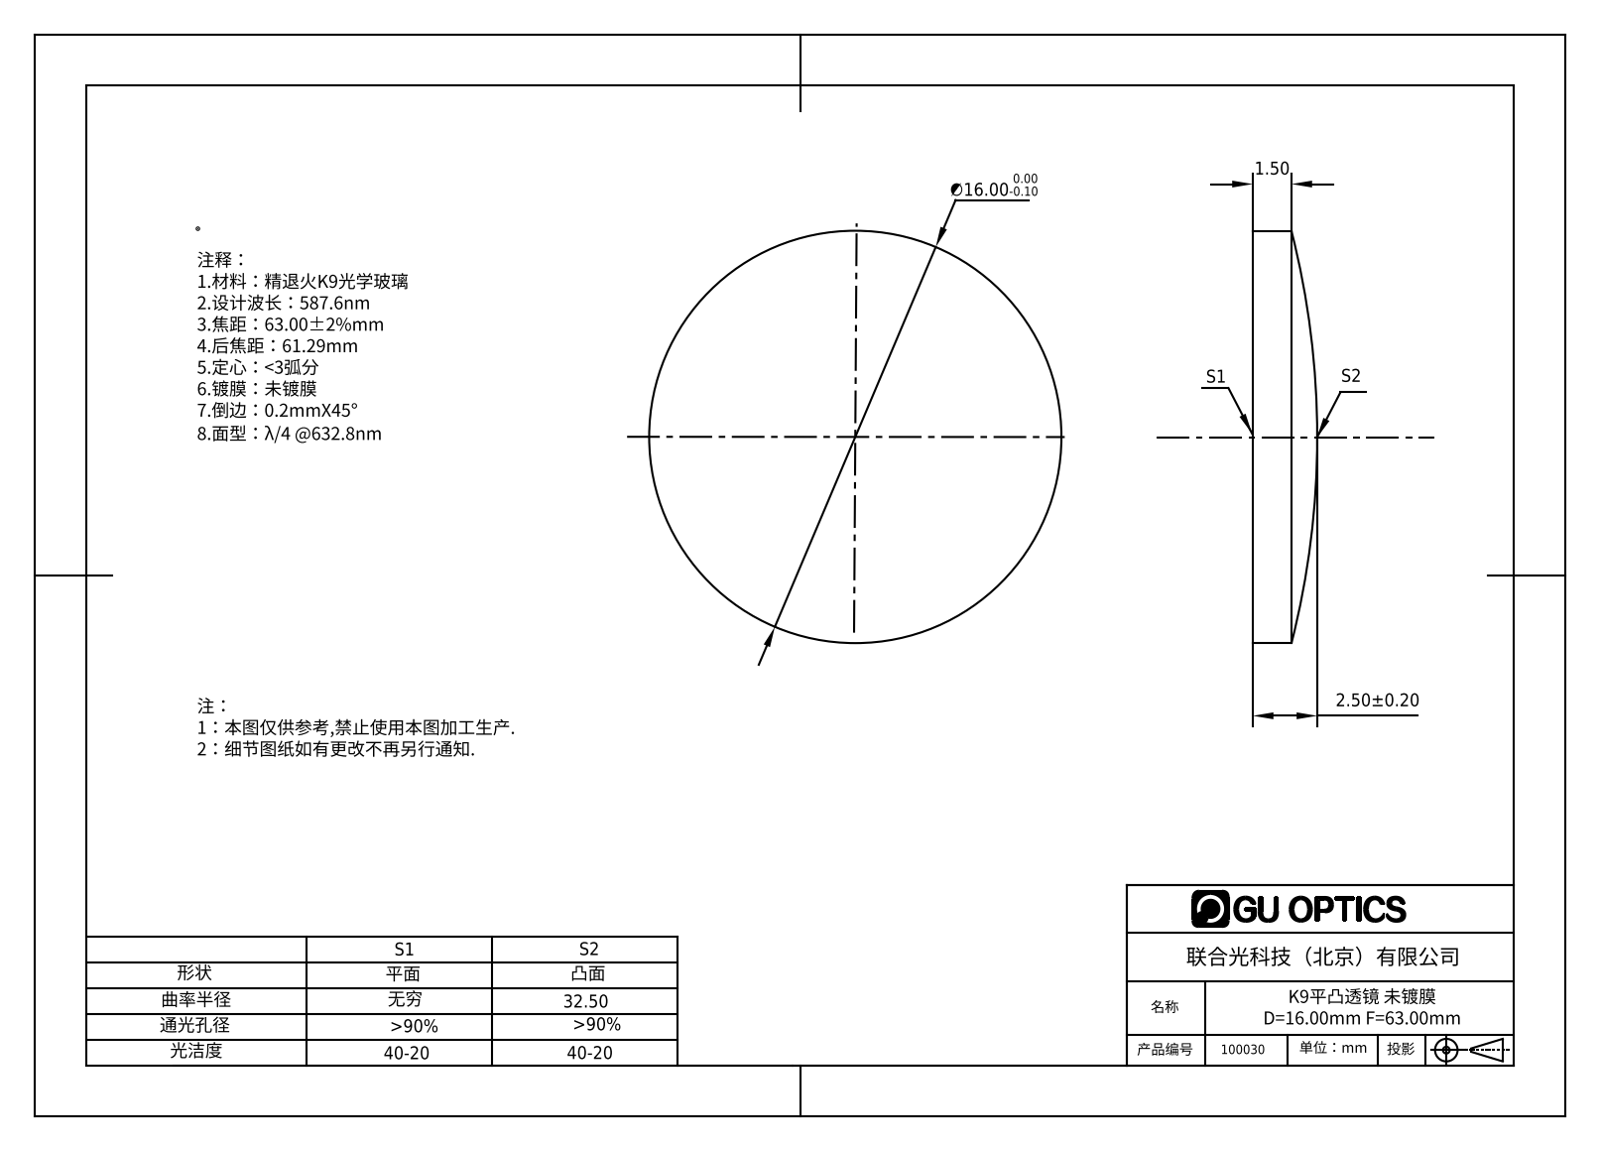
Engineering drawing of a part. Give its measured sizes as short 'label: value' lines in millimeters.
name: 100030
written by: SolidWorks 2016 (AUTOMOTIVE_DESIGN)
unit: mm
bodies: 1 solid, 5 faces (1 planar, 2 cylindrical, 2 other)
size: 16 × 16 × 2.5
volume: 403 mm³; area: 481 mm²
bosses: 1× ⌀16
